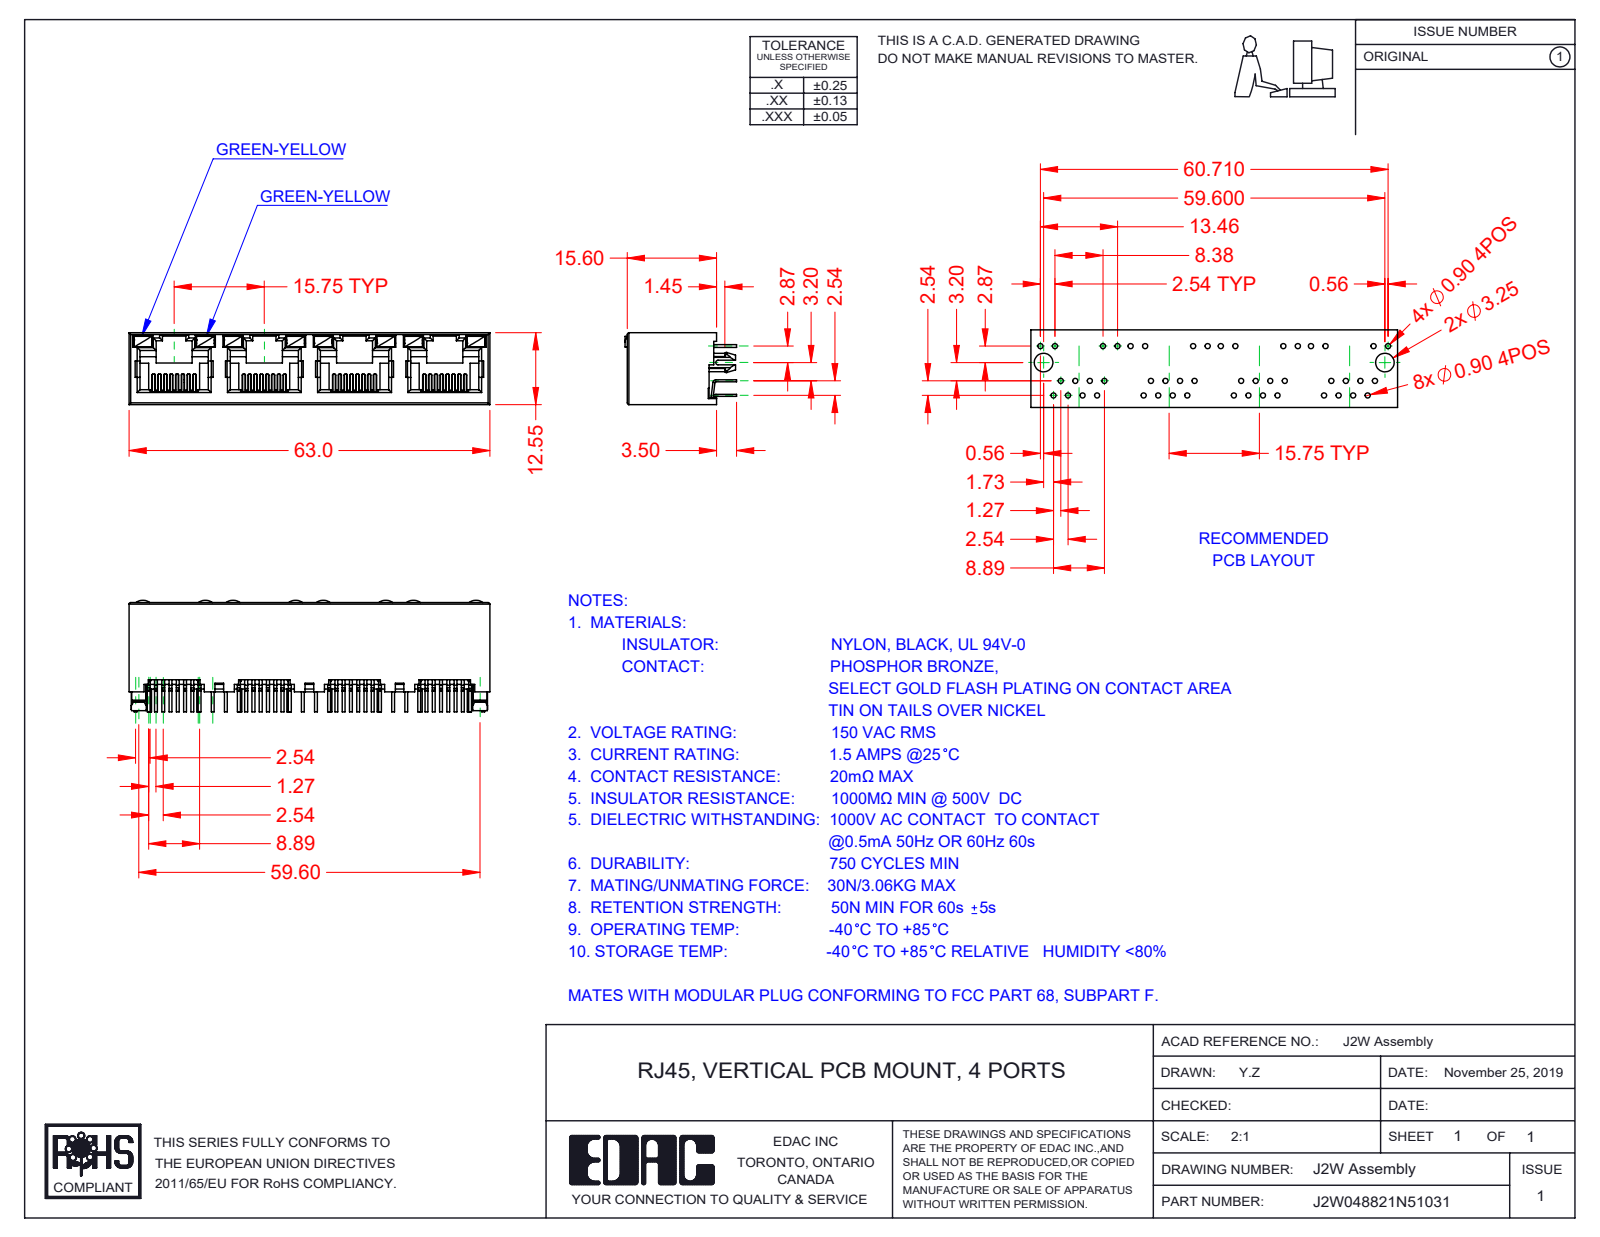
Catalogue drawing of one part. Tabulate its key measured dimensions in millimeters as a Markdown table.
| quantity | value |
| --- | --- |
| part name | J2W048821N55131; 2W LED RH_5-Green-Yellow; 2W LED LH_5-Green-Yellow; 2W Contacts (+2 more) |
| STEP written by | SolidWorks 2016 (CONFIG_CONTROL_DESIGN) |
| units | millimeters |
| bodies | 45 solids, 3143 faces (2600 planar, 485 cylindrical, 58 other) |
| overall size | 63 × 19.5 × 12.55 |
| volume | 5 335 mm³ |
| surface area | 13 144 mm² |
| partial cylindrical surfaces (radius × count) | 0.15 × 64, 0.2 × 29, 0.5 × 28, 0.3 × 14, 0.45 × 8, 2 × 8, 0.25 × 2, 1.5 × 2 |
| main face-to-face distances | 12.55, 11.9, 0.65, 15.75, 0.36, 1.5, 0.78, 0.6, 11.3, 31.5 |
